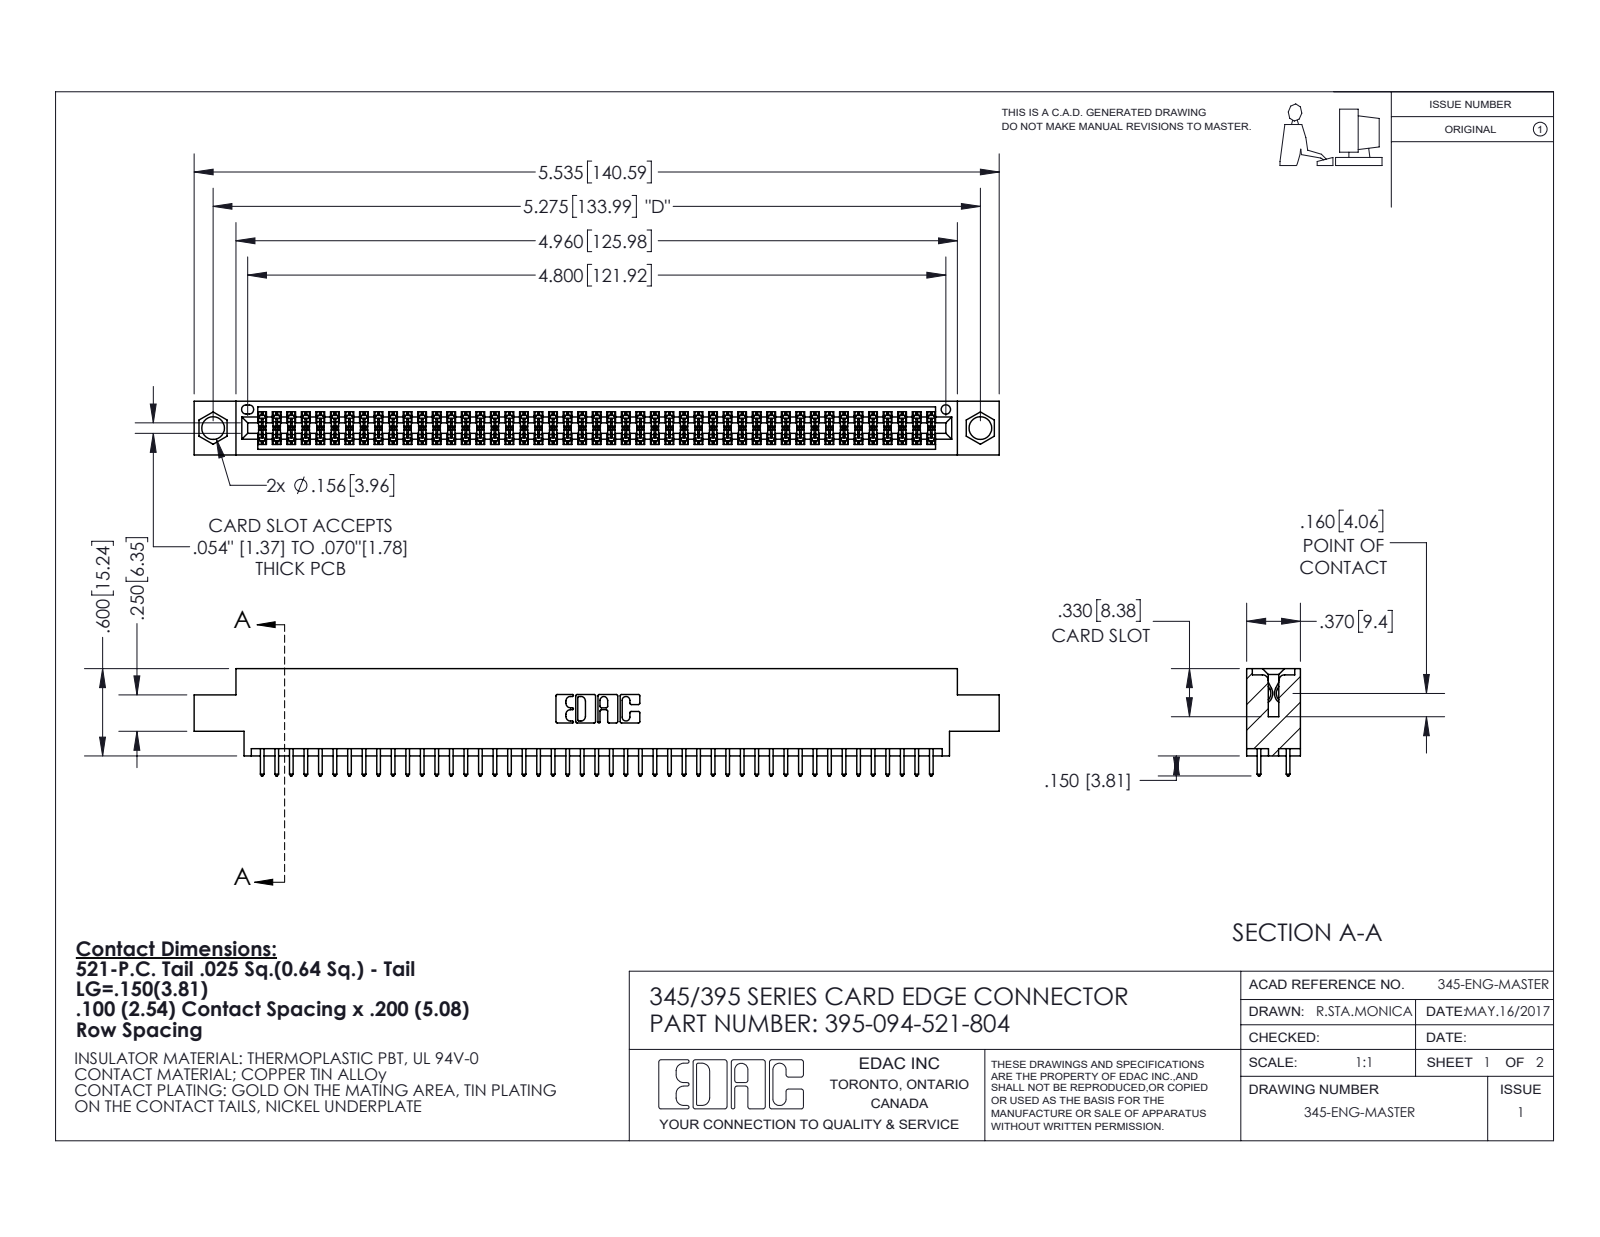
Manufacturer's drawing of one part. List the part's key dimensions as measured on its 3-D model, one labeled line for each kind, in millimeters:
Part name (STEP PRODUCT): 345-292-001_345-293-121; 395-094-521-804; 345 Part_0.170 Offset - 0.156 Dia-TI
STEP written by: SolidWorks 2020 (CONFIG_CONTROL_DESIGN)
Units: millimetres
Bodies: 95 solids, 4844 faces (3200 planar, 1644 cylindrical, 0 other)
Overall size (bounding box): 140.6 × 18.7 × 9.4
Volume: 13 500 mm³ · Surface area: 19 720 mm²
Round holes (diameter × count): ⌀4 ×2, ⌀1.6 ×1
Partial cylindrical surfaces — rounded edges, fillets, slot ends (radius × count): R0.2 ×188, R0.3 ×94, R0.3 ×22, R0.2 ×6, R0.8 ×6, R0.7 ×3, R0.4 ×2, R0.5 ×2
Main face-to-face distances: 1.8, 7.6, 5.1, 9.4, 2.5, 6.9, 0.6, 5.7, 4.4, 3.8
Hole centre spacings: 6.9, 128, 134
